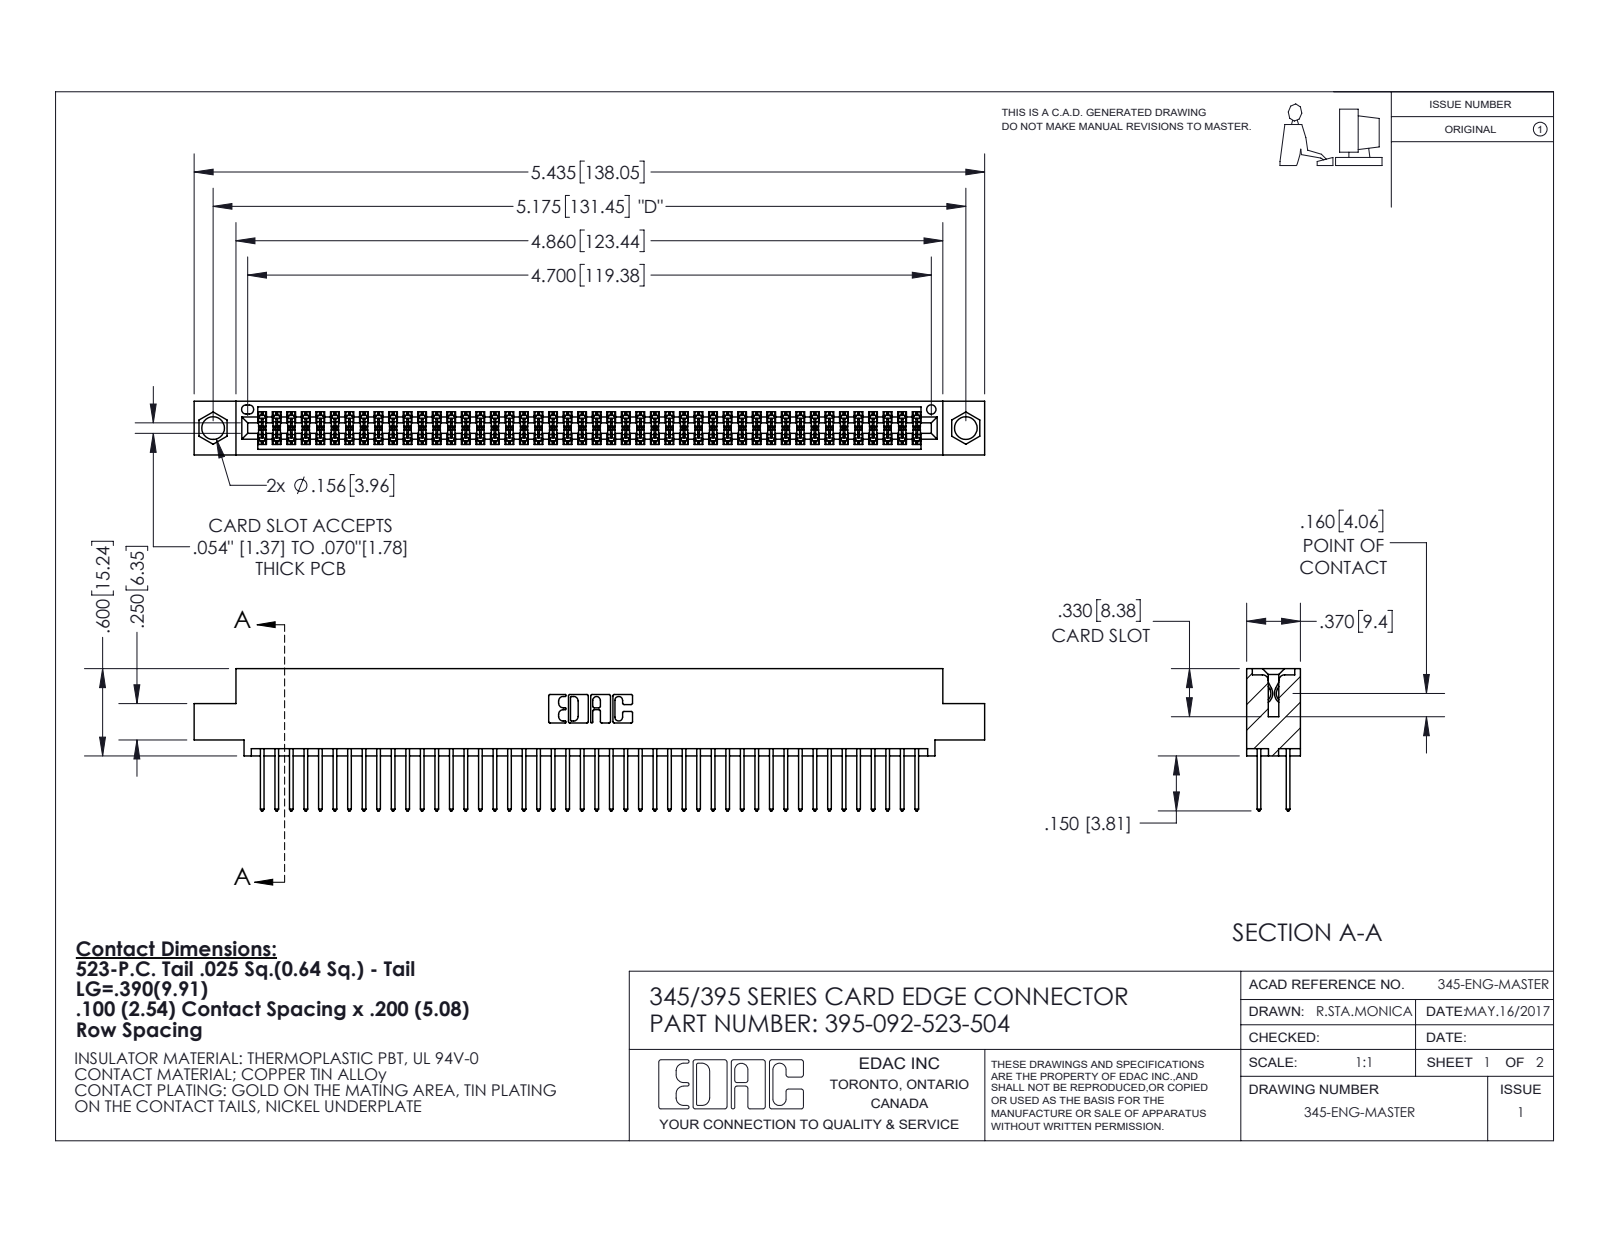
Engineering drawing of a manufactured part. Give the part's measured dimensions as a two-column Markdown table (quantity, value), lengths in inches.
| quantity | value |
| --- | --- |
| part name | 345 Part_0.110 Offset - 0.156 Dia-TI; 345-292-001_345-293-123; 395-092-523-504 |
| STEP written by | SolidWorks 2020 (CONFIG_CONTROL_DESIGN) |
| units | inches |
| bodies | 93 solids, 4744 faces (3134 planar, 1610 cylindrical, 0 other) |
| overall size | 5.435 × 0.977 × 0.37 |
| volume | 0.821 in³ |
| surface area | 32.18 in² |
| round holes (diameter × count) | 0.156 × 2, 0.064 × 1 |
| partial cylindrical surfaces (radius × count) | 0.006 × 184, 0.01 × 92, 0.01 × 22, 0.007 × 6, 0.031 × 6, 0.026 × 3, 0.014 × 2, 0.019 × 2 |
| main face-to-face distances | 0.072, 0.298, 0.2, 0.098, 0.272, 0.025, 0.37, 0.225, 0.175, 0.149 |
| hole center spacings | 0.27, 4.939, 5.175 |
